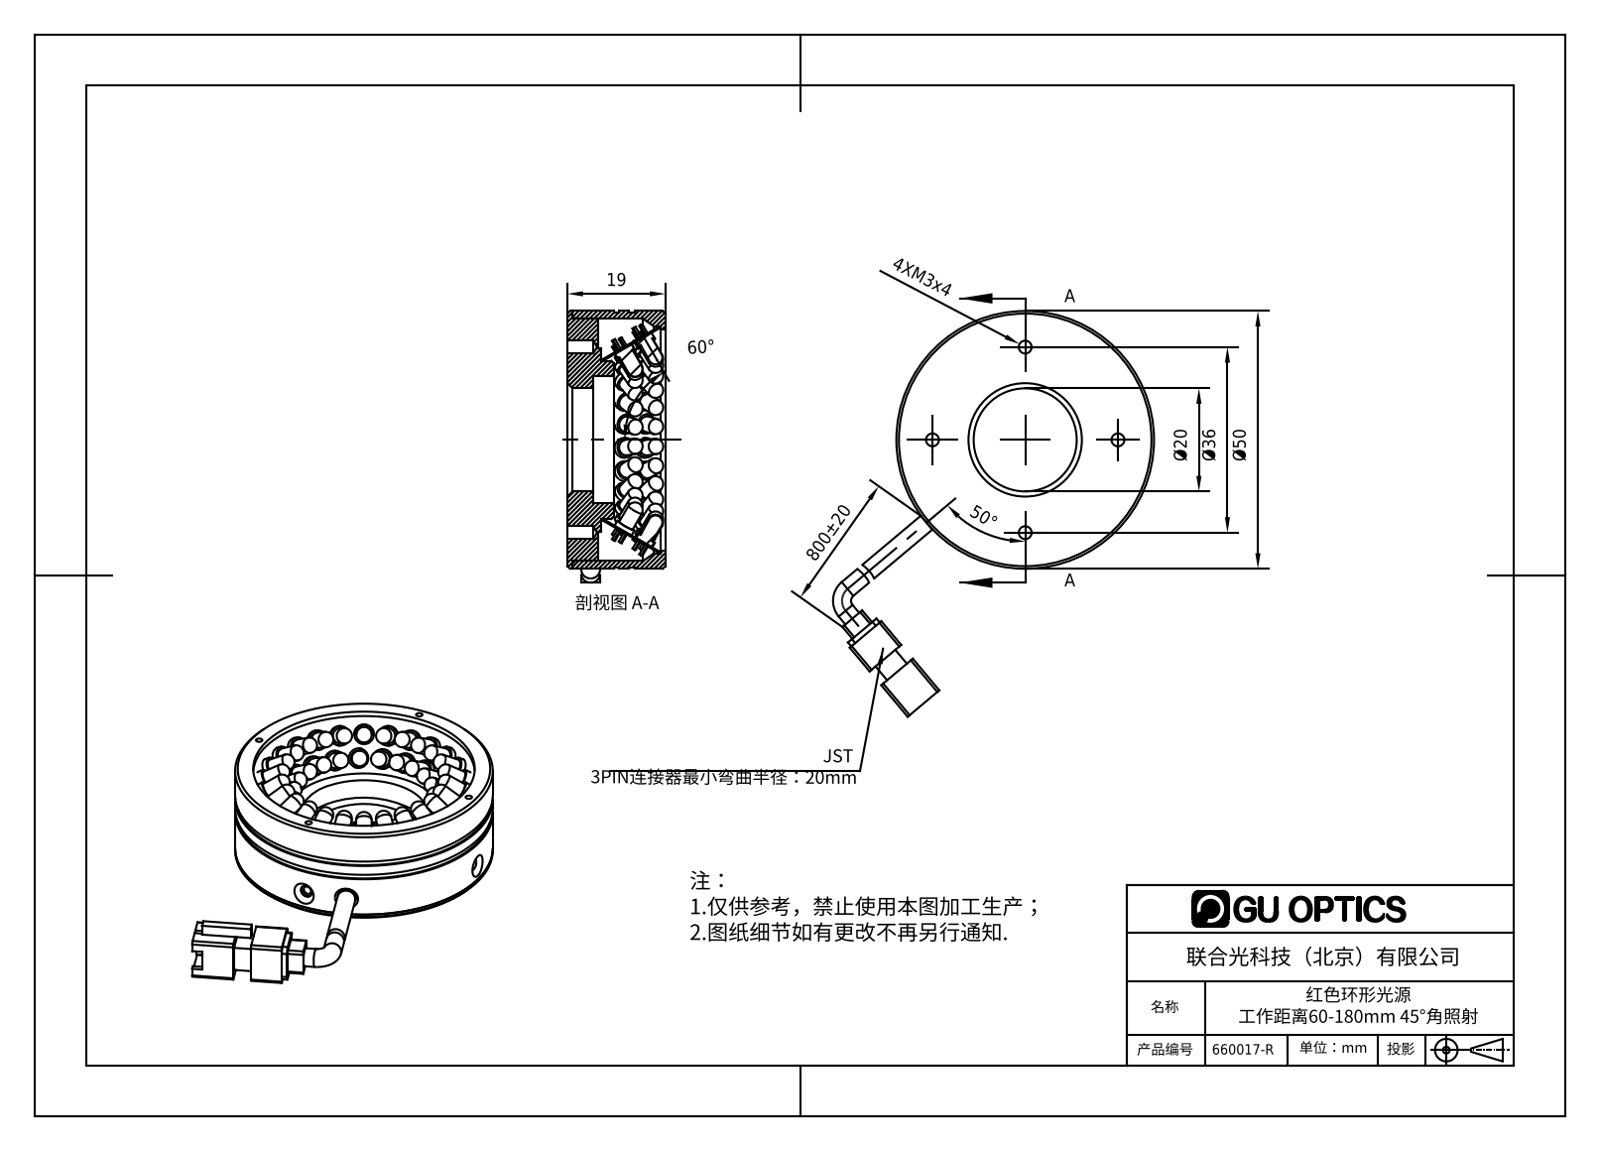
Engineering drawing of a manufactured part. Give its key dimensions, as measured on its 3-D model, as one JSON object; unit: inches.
{"part_name": "660017-R", "step_written_by": "SolidWorks 2016 (AUTOMOTIVE_DESIGN)", "units": "inches", "bodies": {"solids": 54, "faces": 1066, "planar": 662, "cylindrical": 300, "other": 104}, "overall_size": [3.265, 1.969, 0.748], "volume_in3": 1.076, "surface_area_in2": 31.4, "round_holes": [[0.049, 4], [0.098, 4], [0.063, 2], [0.094, 2], [0.118, 2], [0.142, 1], [0.787, 1], [0.969, 1], [1.693, 1], [1.732, 1]], "round_bosses_or_shafts": [[0.15, 49], [0.118, 47], [0.138, 2], [1.969, 1], [1.945, 1], [1.85, 1], [1.399, 1], [1.209, 1]], "partial_cylinders_radius": [[0.02, 12], [0.039, 4], [0.157, 1]], "face_to_face_distances": [0.039, 0.236, 0.02, 0.197, 0.217, 0.315, 0.118, 0.512, 0.098, 0.059], "hole_center_spacings": [0.459, 0.825, 0.906, 1.281, 0.709, 1.002, 1.402, 1.56]}
